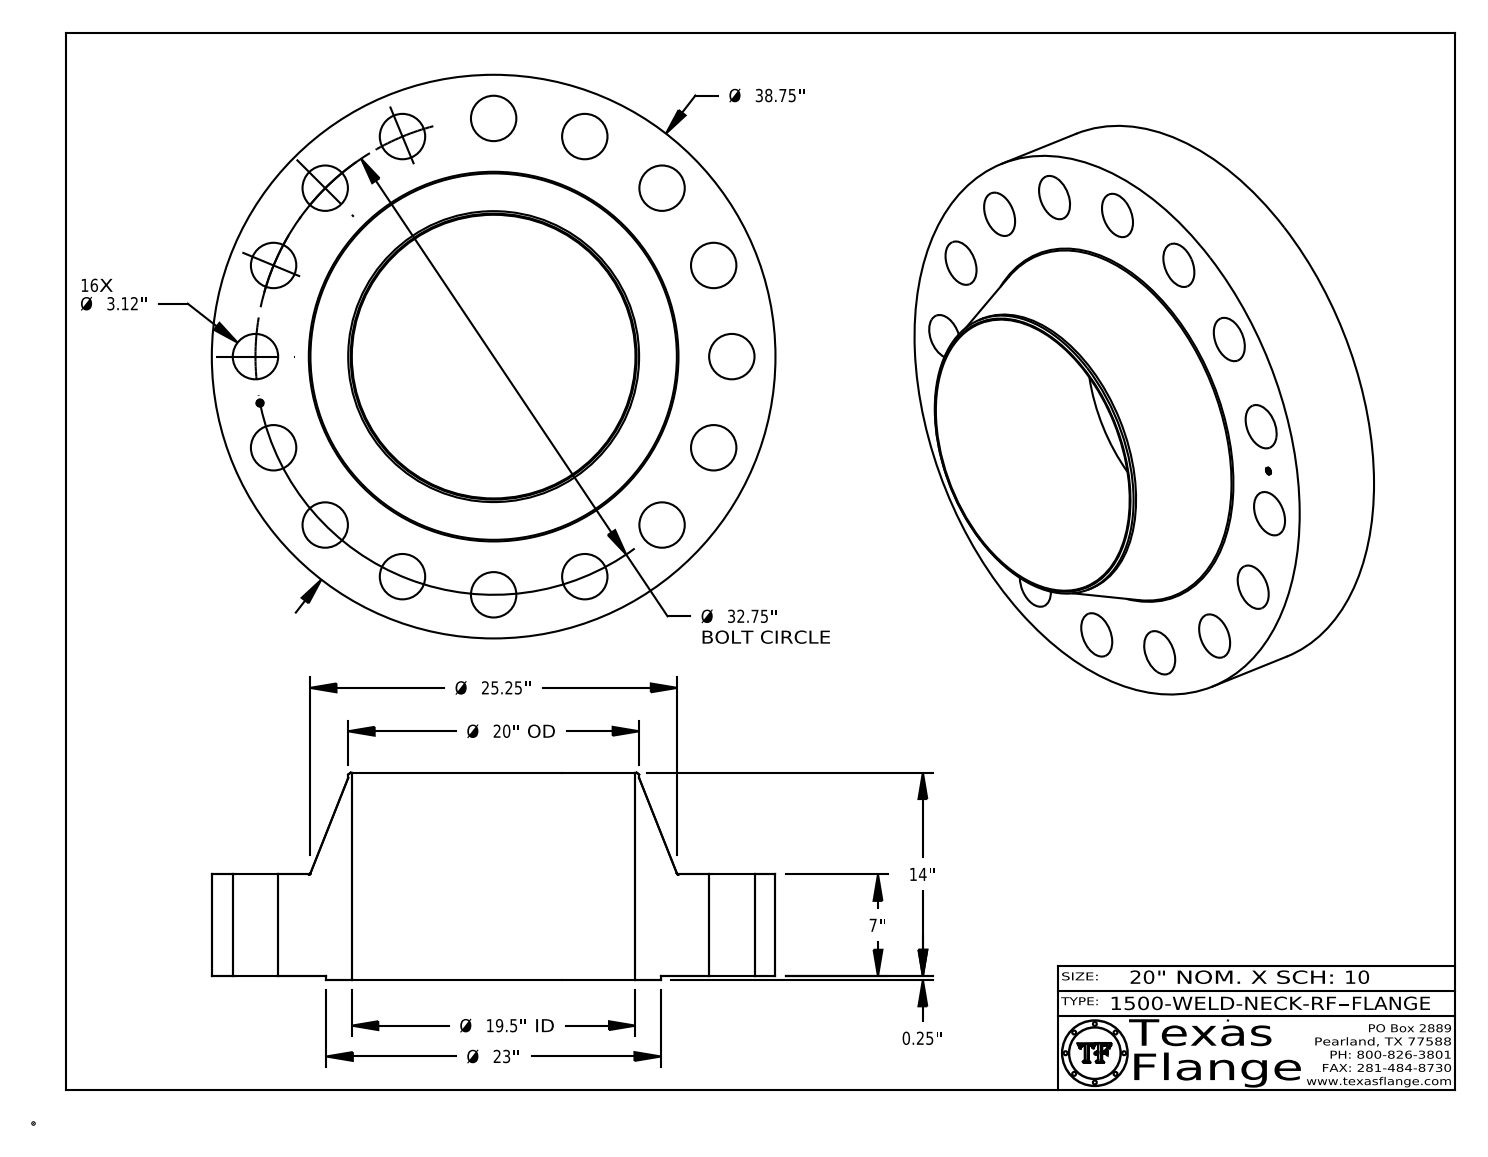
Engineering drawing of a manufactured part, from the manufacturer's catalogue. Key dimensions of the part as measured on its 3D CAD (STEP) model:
Part name (STEP PRODUCT): 1500-WELD-NECK-RF
STEP written by: CATIA V5 STEP AP214 (AUTOMOTIVE_DESIGN)
Units: inches
Bodies: 1 solid, 435 faces (369 planar, 60 cylindrical, 6 other)
Overall size (bounding box): 38.75 × 38.75 × 14.25
Volume: 6 040 in³ · Surface area: 4 694 in²
Round holes (diameter × count): ⌀3.12 ×16, ⌀0.495 ×1, ⌀19.5 ×1
Round bosses / shafts (diameter × count): ⌀0.03 ×8, ⌀38.75 ×1, ⌀23 ×1, ⌀20 ×1, ⌀0.39 ×1
Main face-to-face distances: 7, 0.25, 7.25, 14.25, 14, 7.235, 6.985, 0.015, 7.015, 0.148
Hole centre spacings: 18.195, 16.375, 12.533, 23.157, 30.257, 6.389, 6.389, 27.23
